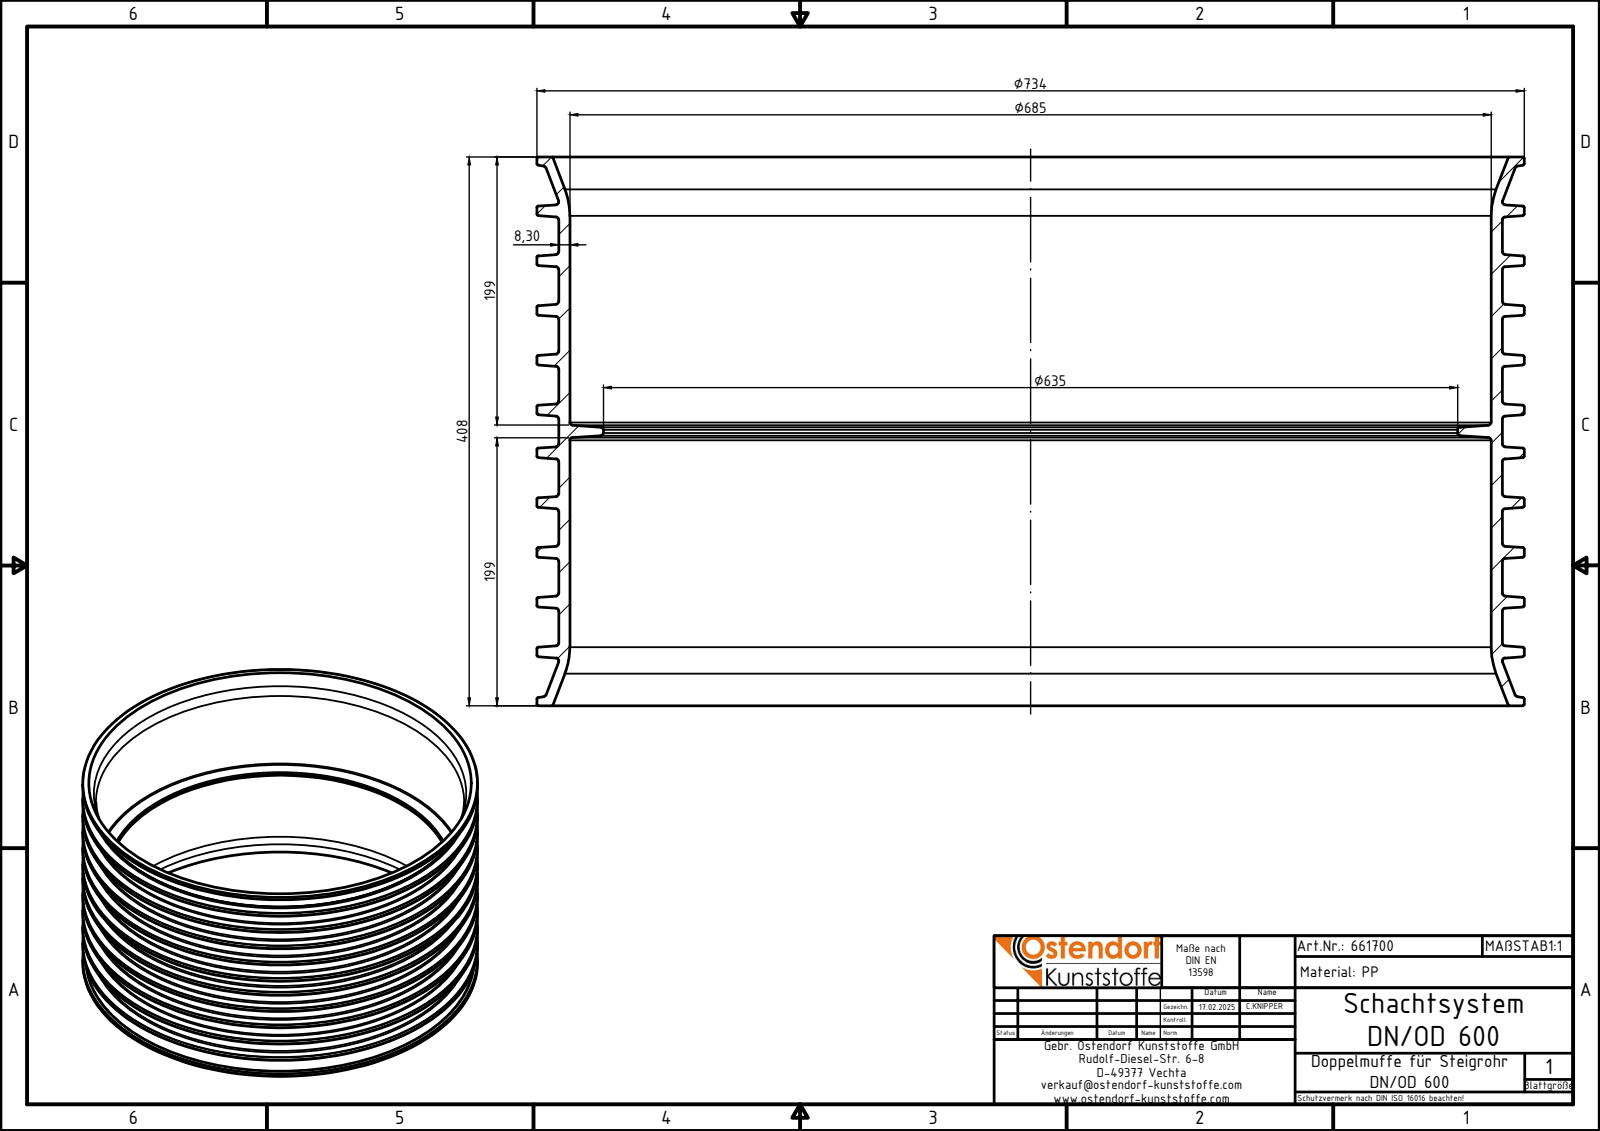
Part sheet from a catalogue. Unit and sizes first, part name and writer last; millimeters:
Units: millimetres
Overall size (bounding box): 734 × 734 × 408
Round holes (diameter × count): ⌀635 ×1, ⌀685 ×1
Round bosses / shafts (diameter × count): ⌀734 ×1, ⌀701.6 ×1
Main face-to-face distances: 408
Volume: 10 870 000 mm³ · Surface area: 2 604 000 mm²
Bodies: 1 solid, 110 faces (2 planar, 26 cylindrical, 82 other)
Part name (STEP PRODUCT): 661700z
STEP written by: Autodesk Inventor 2024 (AUTOMOTIVE_DESIGN)
